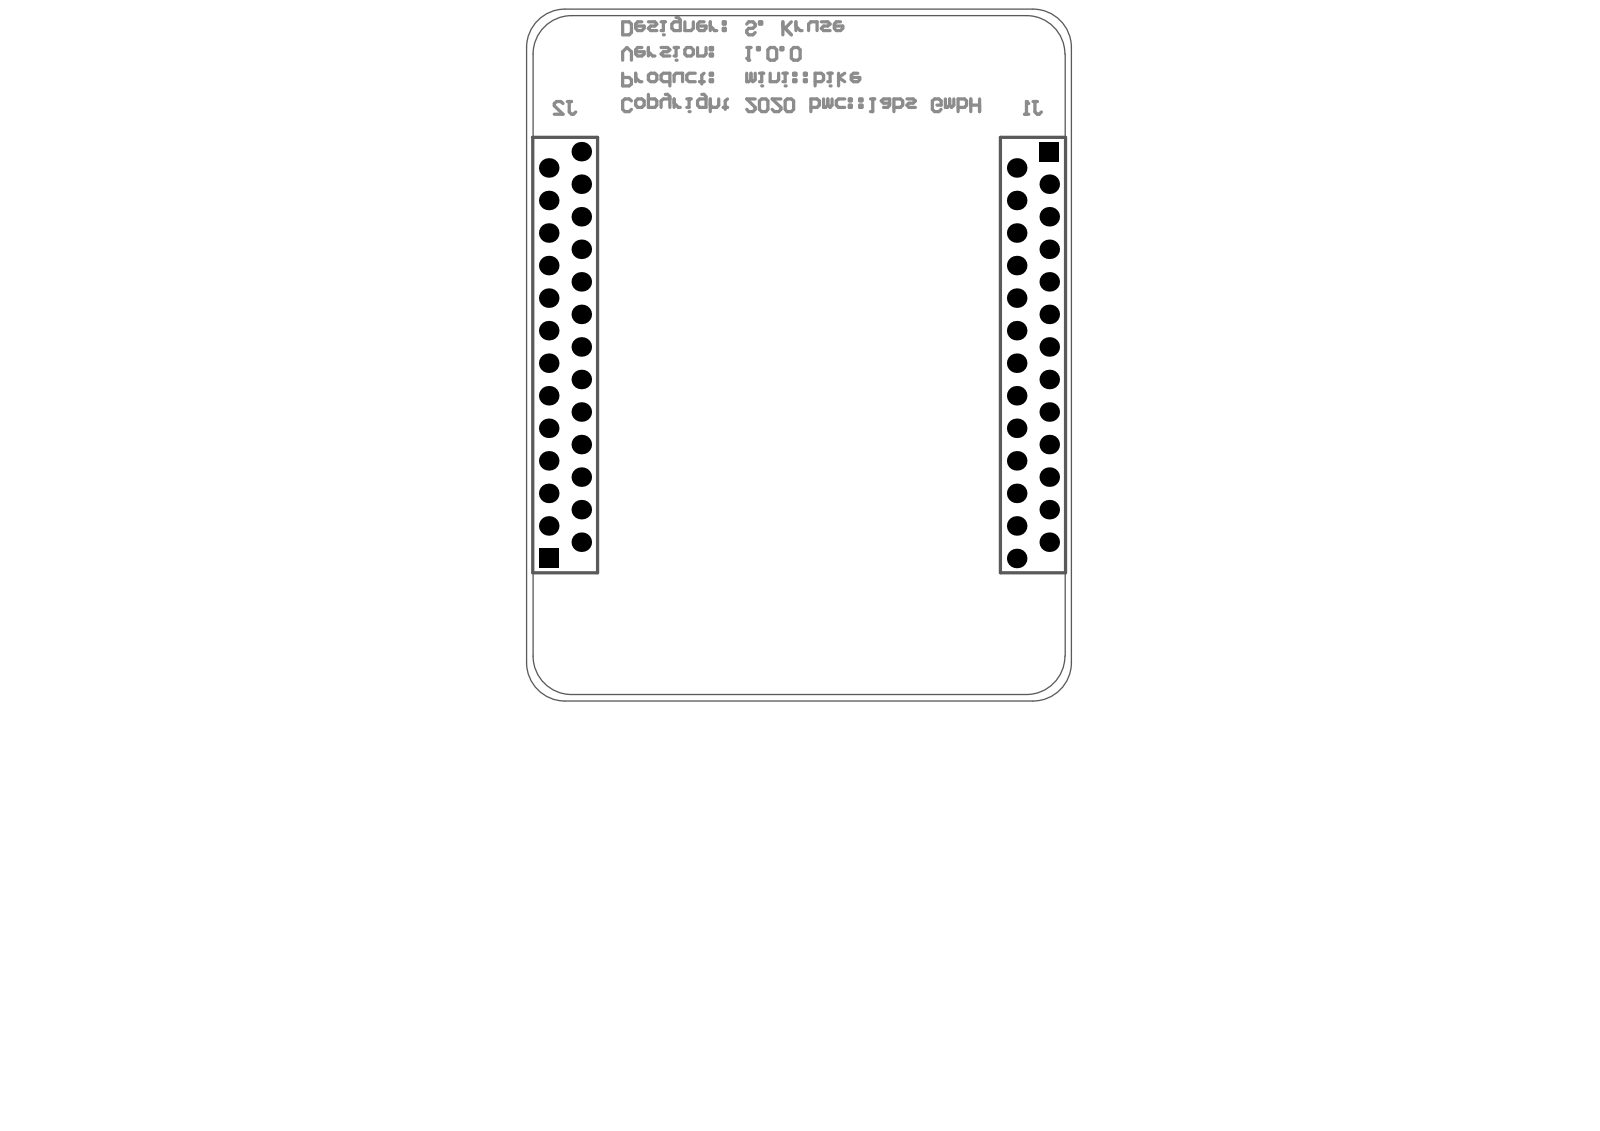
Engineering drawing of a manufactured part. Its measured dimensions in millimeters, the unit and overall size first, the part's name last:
Units: millimetres
Overall size (bounding box): 86.77 × 42.69 × 29.69
Round holes (diameter × count): ⌀0.8 ×52, ⌀1.5 ×8, ⌀3.2 ×4, ⌀4 ×2
Round bosses / shafts (diameter × count): ⌀3.7 ×2
Partial cylindrical surfaces — rounded edges, fillets, slot ends (radius × count): R0.1 ×316, R0.3 ×16, R0.12 ×8, R0.55 ×8, R0.7 ×8, R0.95 ×8, R0.25 ×7, R2 ×5
Main face-to-face distances: 1.65, 0.4, 2.05, 36.5, 1.5, 6, 1.7, 1.3, 1.1, 0.45
Hole centre spacings: 2.84, 4.58, 5.08, 10.16, 6.84, 9.25, 14.2, 2.55
Volume: 12 123 mm³ · Surface area: 16 429 mm²
Bodies: 70 solids, 3319 faces (2323 planar, 917 cylindrical, 79 other)
Part name (STEP PRODUCT): PCB; Board; J3; 348300801 (+8 more)
STEP written by: Open CASCADE 6.5 (AUTOMOTIVE_DESIGN)
